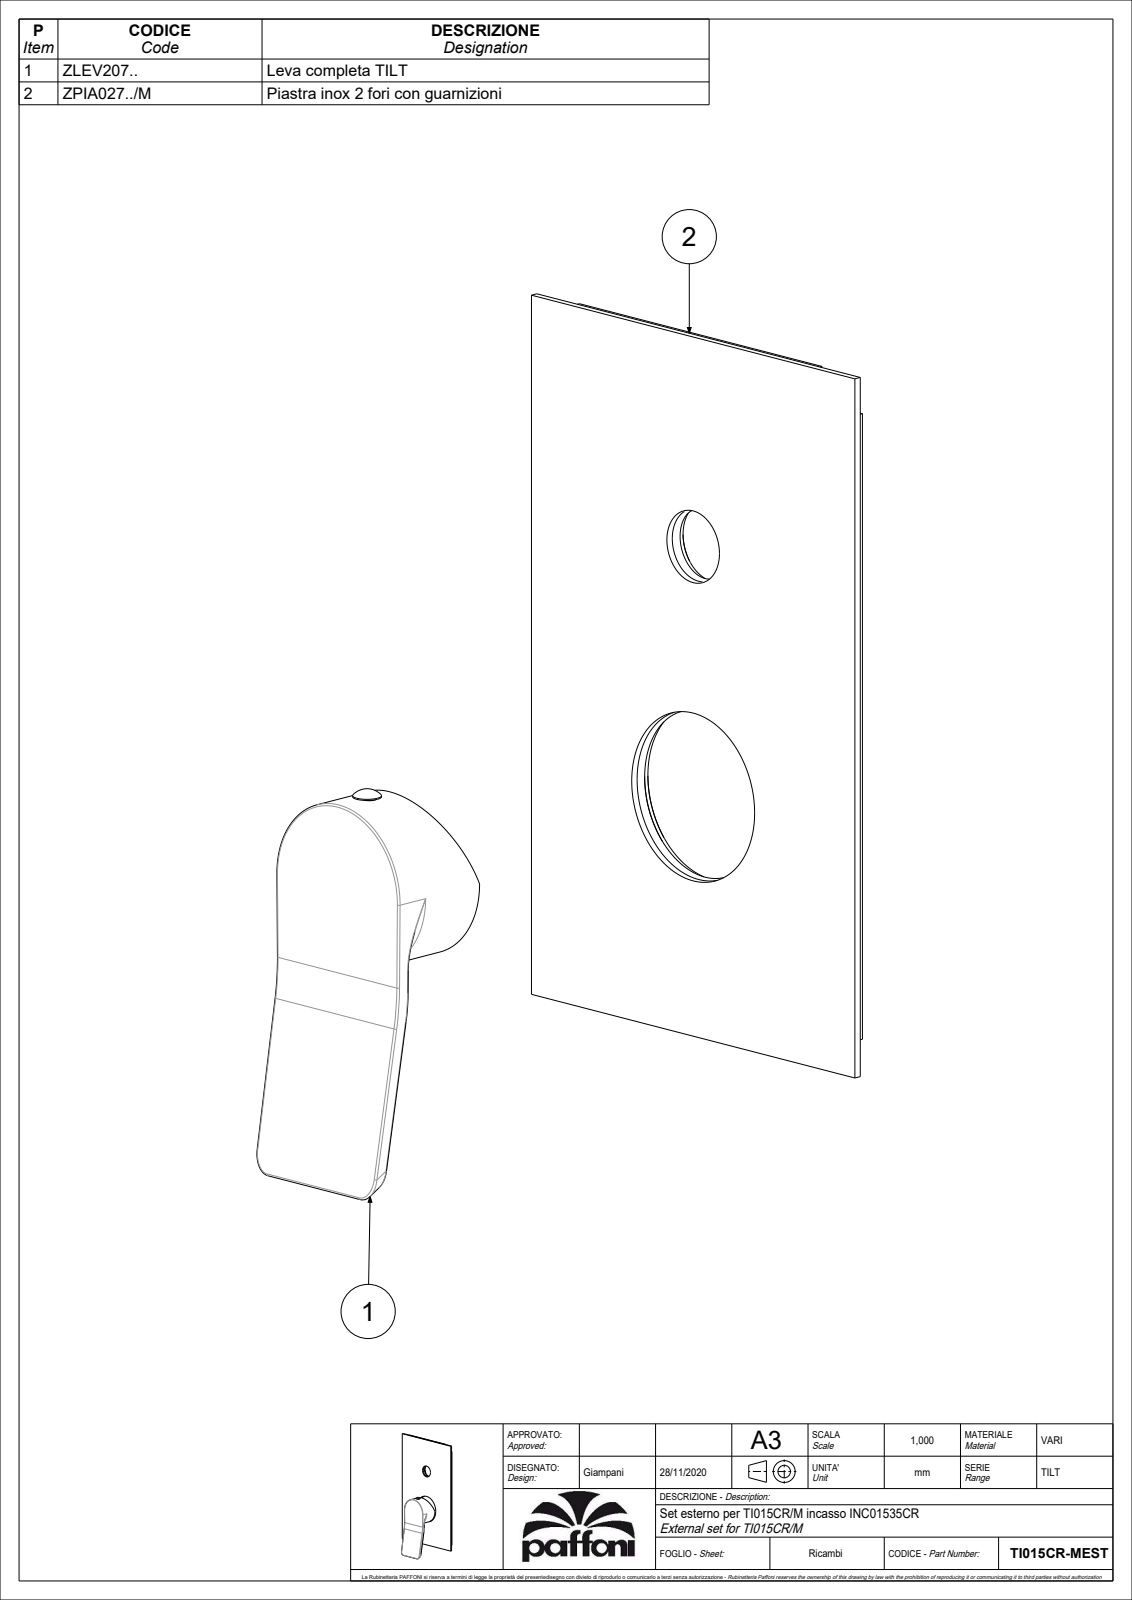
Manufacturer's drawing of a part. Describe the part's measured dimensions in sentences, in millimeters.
The part is named "TI015CR-MEST". Its 3-D file was written by "CREO PARAMETRIC BY PTC INC, 2020044 (CONFIG_CONTROL_DESIGN)". It is 2 solids with 169 faces: 74 planar, 54 cylindrical and 41 other. Overall it measures 204.58 by 120 by 48.45 millimeters. Its volume is 76 468 cubic millimeters and its surface area 66 158 square millimeters. Round holes: 1 of diameter 3, 1 of diameter 19.5, 1 of diameter 21.5, 1 of diameter 25, 1 of diameter 45.6, 1 of diameter 47.6, 1 of diameter 51.1. Round bosses or shafts: 1 of diameter 54.6, 1 of diameter 45.5, 1 of diameter 28.5, 1 of diameter 7.6, 1 of diameter 5.5, 1 of diameter 5. Partial cylindrical surfaces (rounded edges, fillets, slot ends): 10 of radius 0.5, 2 of radius 1.5, 2 of radius 5, 1 of radius 44.14, 1 of radius 63. The main face-to-face distances are 2, 0.8, 2.8, 4.01, 34.8, 34, 32, 4, 30, 30.8. The hole center spacings are 68.
